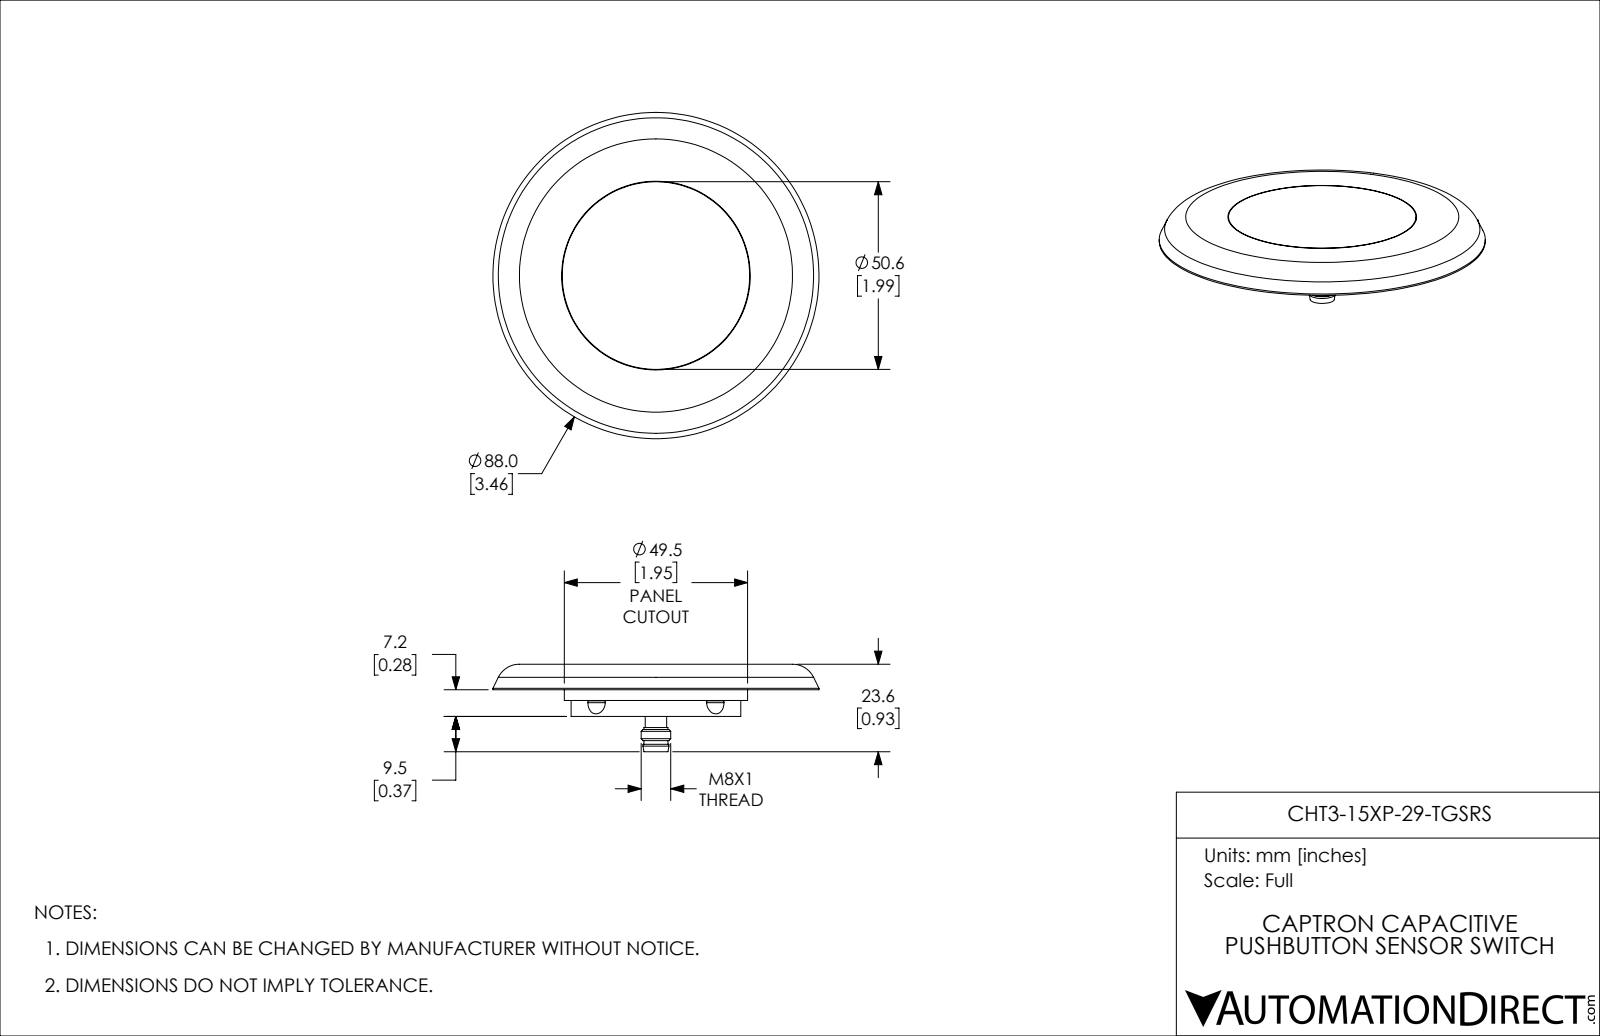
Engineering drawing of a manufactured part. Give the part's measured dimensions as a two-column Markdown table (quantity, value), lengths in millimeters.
| quantity | value |
| --- | --- |
| part name | CHT3-15XP-29-TGSRS |
| STEP written by | SolidWorks 2019 (CONFIG_CONTROL_DESIGN) |
| units | millimeters |
| bodies | 9 solids, 87 faces (25 planar, 36 cylindrical, 26 other) |
| overall size | 88 × 88 × 23.6 |
| volume | 49 670 mm³ |
| surface area | 21 540 mm² |
| round holes (diameter × count) | 6 × 1, 46.1 × 1, 50.9 × 1 |
| round bosses / shafts (diameter × count) | 1 × 4, 50.6 × 1, 49.5 × 1, 45.8 × 1, 8 × 1, 7 × 1, 6.5 × 1, 5.8 × 1 |
| partial cylindrical surfaces (radius × count) | 5 × 4, 0.9 × 1 |
| main face-to-face distances | 6.9, 4.6, 2.3, 7.2, 11.8, 14.1, 0.5, 7.5, 7.7, 4.3 |
